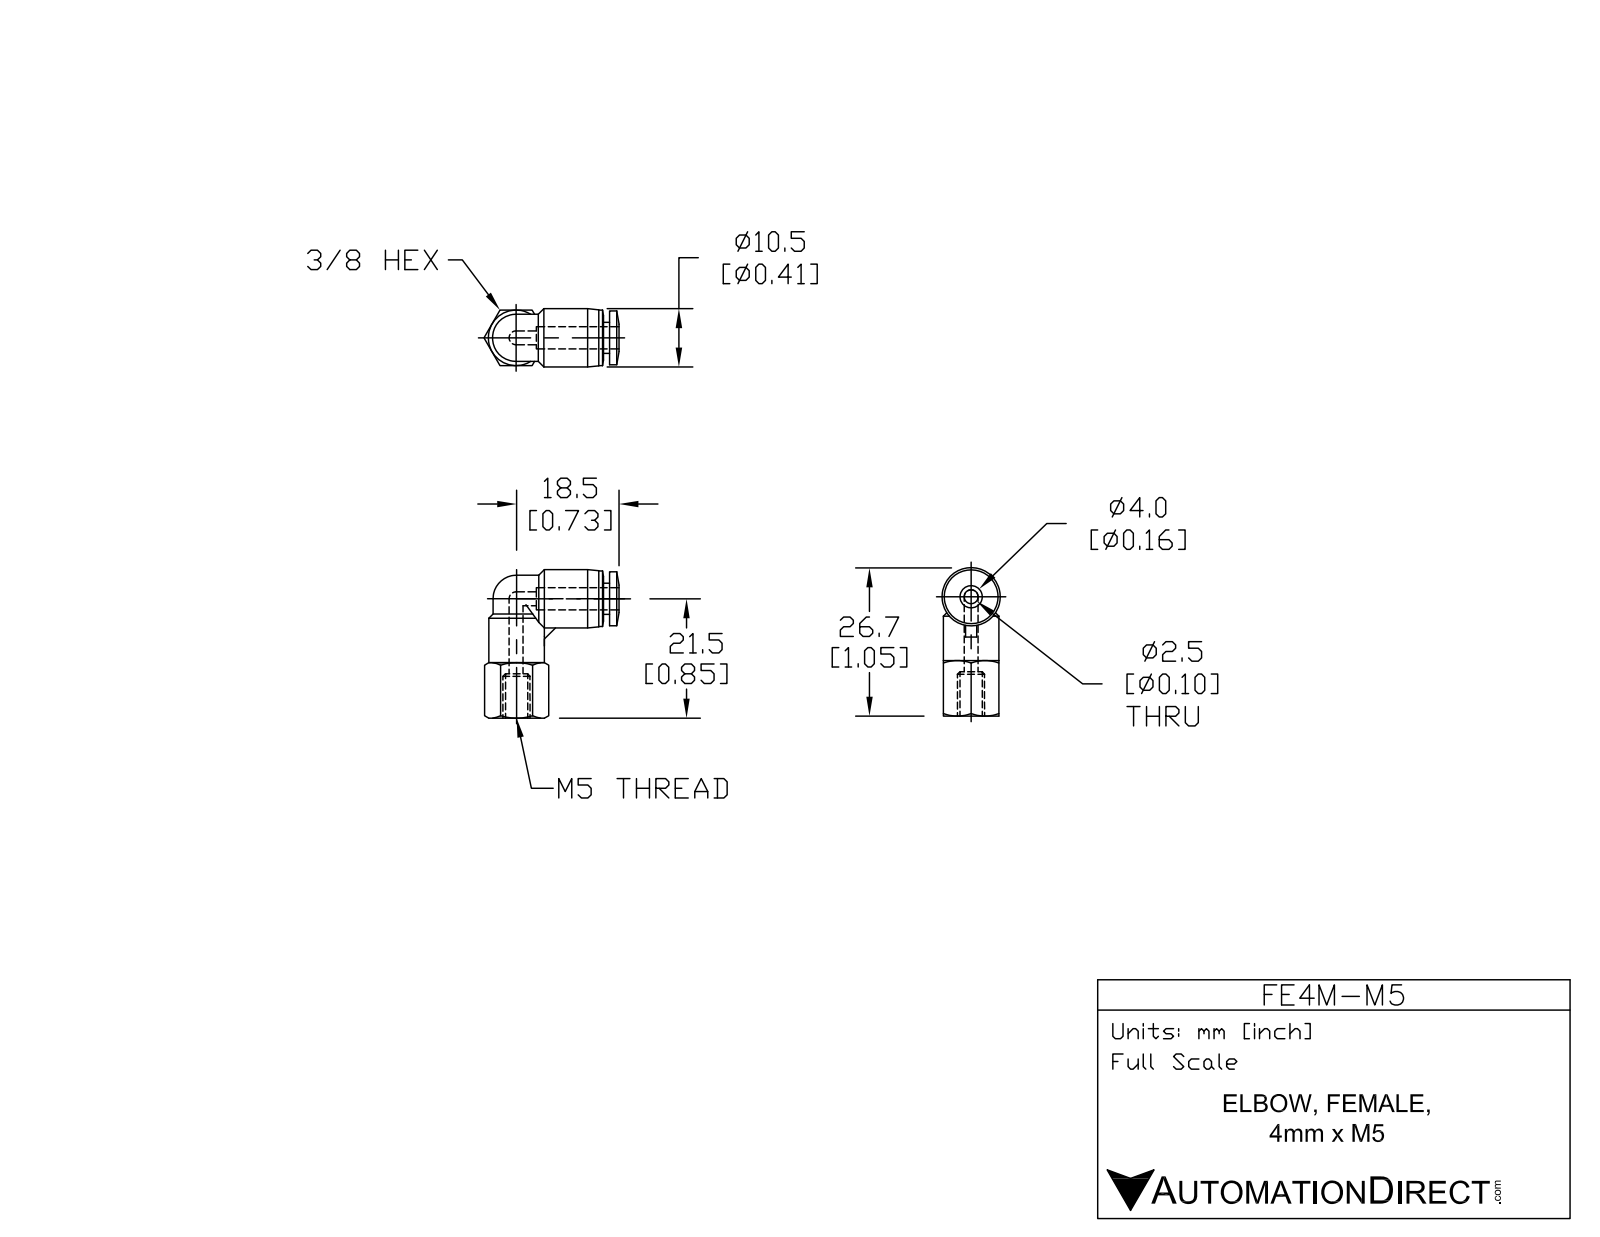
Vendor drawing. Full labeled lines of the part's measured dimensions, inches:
Part name (STEP PRODUCT): FE4M-M5
STEP written by: SolidWorks 2015 (AUTOMOTIVE_DESIGN)
Units: inches
Bodies: 1 solid, 66 faces (16 planar, 21 cylindrical, 29 other)
Overall size (bounding box): 1.053 × 0.954 × 0.413
Volume: 0.154 in³ · Surface area: 3.042 in²
Round holes (diameter × count): ⌀0.118 ×2, ⌀0.169 ×1, ⌀0.197 ×1
Round bosses / shafts (diameter × count): ⌀0.394 ×2, ⌀0.413 ×1, ⌀0.382 ×1, ⌀0.22 ×1
Partial cylindrical surfaces — rounded edges, fillets, slot ends (radius × count): R0.167 ×2
Main face-to-face distances: 0.394, 0.043, 0.315, 0.472, 0.516, 0.157, 0.236, 0.079, 0.439, 0.033
